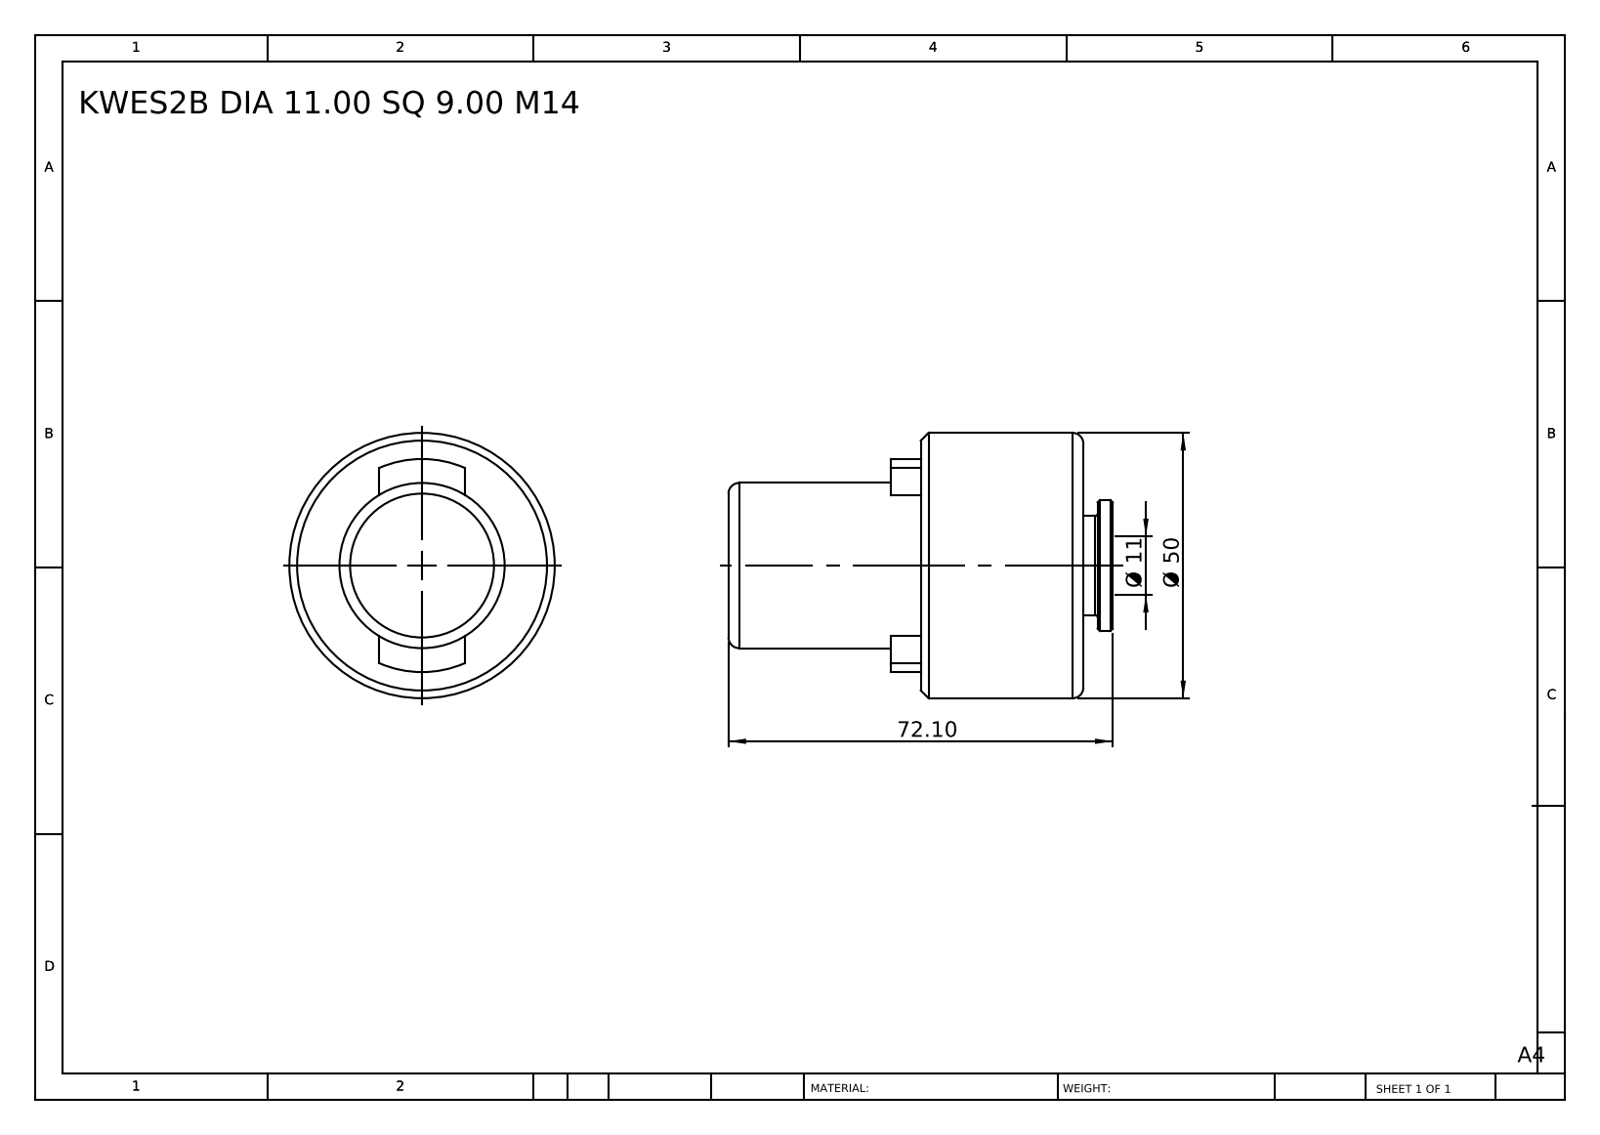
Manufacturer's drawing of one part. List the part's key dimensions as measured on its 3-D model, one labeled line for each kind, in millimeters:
Part name (STEP PRODUCT): KWES2B DIA 11.00 SQ 9.00 1-4'''''''' G(BSP)
STEP written by: SolidWorks 2014 (CONFIG_CONTROL_DESIGN)
Units: millimetres
Bodies: 1 solid, 38 faces (12 planar, 12 cylindrical, 14 other)
Overall size (bounding box): 72.1 × 49.8 × 49.8
Volume: 86 615 mm³ · Surface area: 13 584 mm²
Round holes (diameter × count): ⌀11 ×1
Round bosses / shafts (diameter × count): ⌀49.8 ×1, ⌀31 ×1, ⌀24.5 ×1, ⌀18.6 ×1
Partial cylindrical surfaces — rounded edges, fillets, slot ends (radius × count): R20 ×1
Main face-to-face distances: 30.5, 36.1, 66.6, 72.1, 36, 5.5, 30.4, 5.7, 36.2, 41.7
